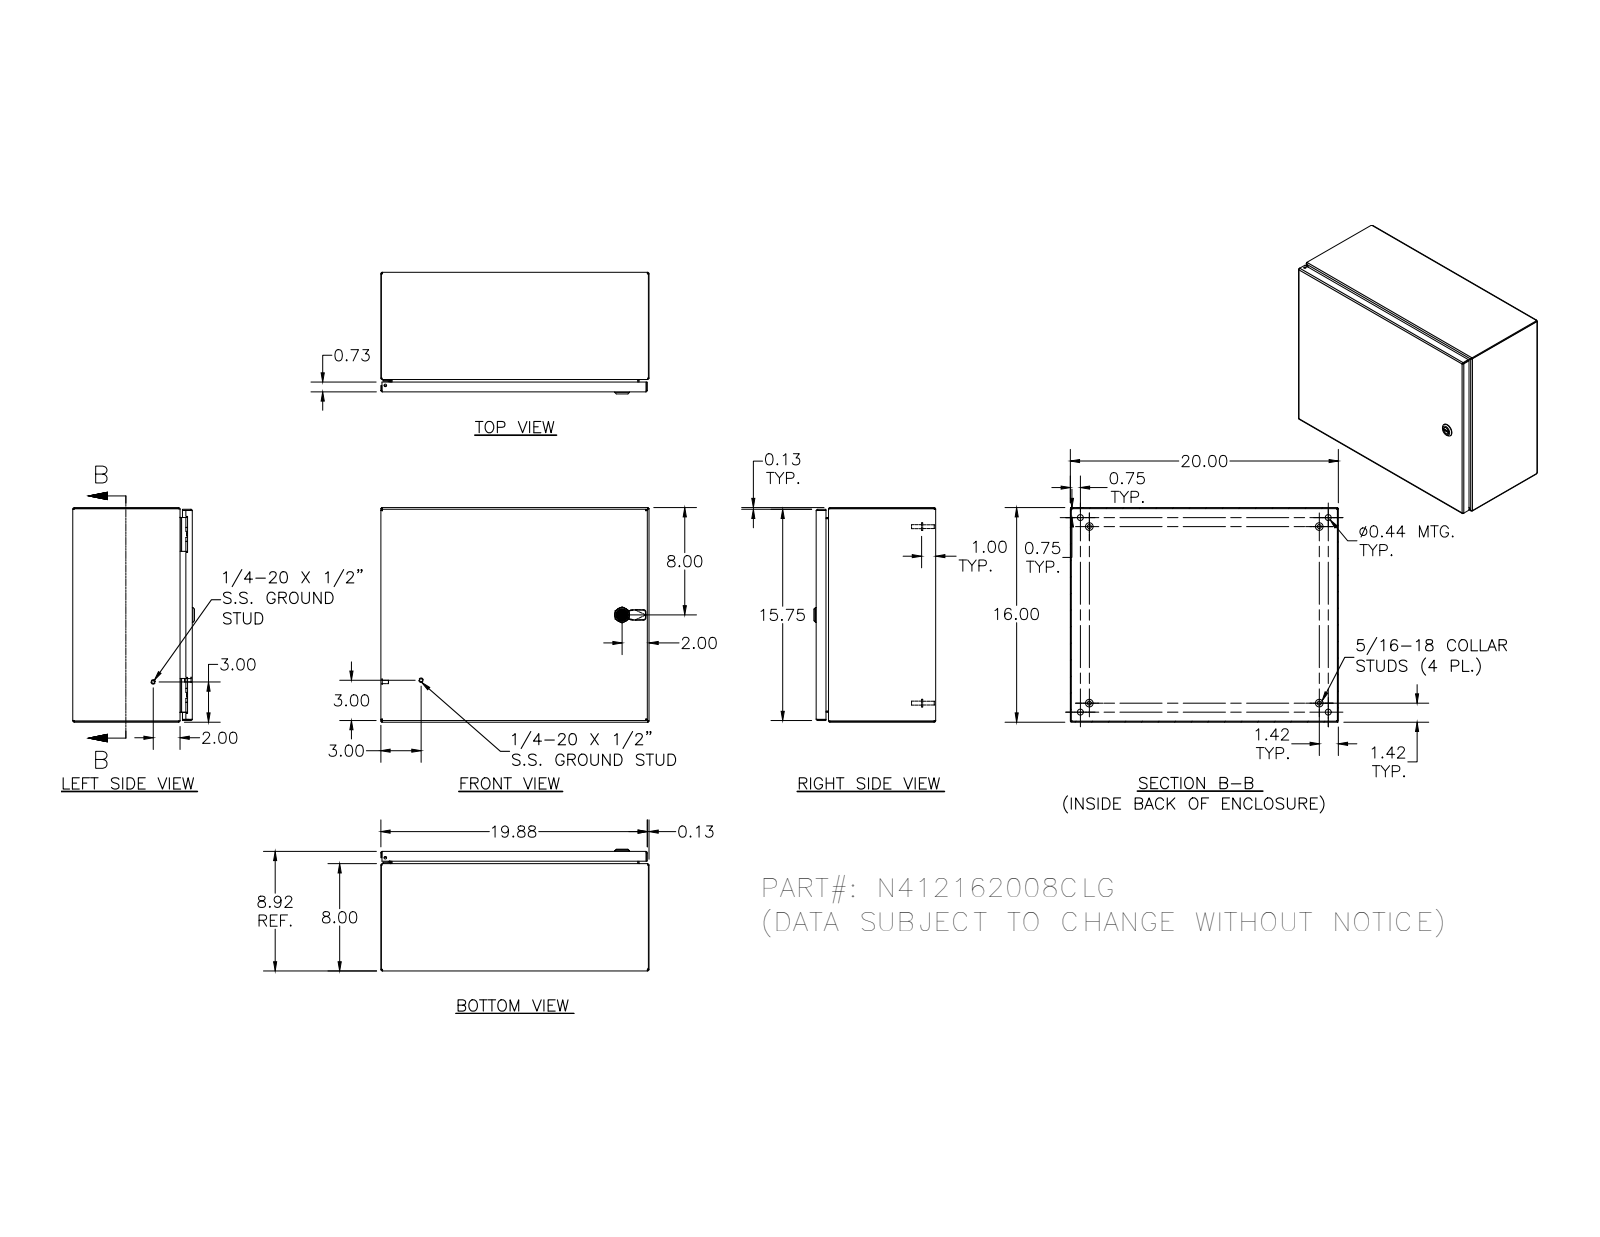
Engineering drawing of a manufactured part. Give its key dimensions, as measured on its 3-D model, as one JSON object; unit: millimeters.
{"part_name": "N412162008CLG", "step_written_by": "SolidWorks 2018 (AUTOMOTIVE_DESIGN)", "units": "millimeters", "bodies": {"solids": 33, "faces": 1449, "planar": 530, "cylindrical": 547, "other": 372}, "overall_size": [508, 406.4, 230.5], "volume_mm3": 1655000, "surface_area_mm2": 1773000, "round_holes": [[4.8, 5], [2.4, 4], [3.9, 4], [4.2, 4], [4.4, 4], [11.1, 4], [4, 2], [4.7, 1], [5, 1], [8, 1], [10, 1], [10.2, 1]], "round_bosses_or_shafts": [[6.4, 10], [14.3, 4], [9.1, 4], [8.1, 4], [7.6, 4], [7, 4], [6.5, 4], [4.2, 4]], "partial_cylinders_radius": [[0.3, 30], [0.8, 30], [1.3, 26], [2.7, 20], [0.4, 18], [3.2, 16], [0.5, 13], [0.8, 8]], "face_to_face_distances": [1.9, 224.6, 222.7, 226.5, 1.9, 404.5, 406.4, 402.6, 404.5, 506.1], "hole_center_spacings": [304.8, 16.8, 16.7, 33.2, 49.9, 288, 304.7, 321.5]}
